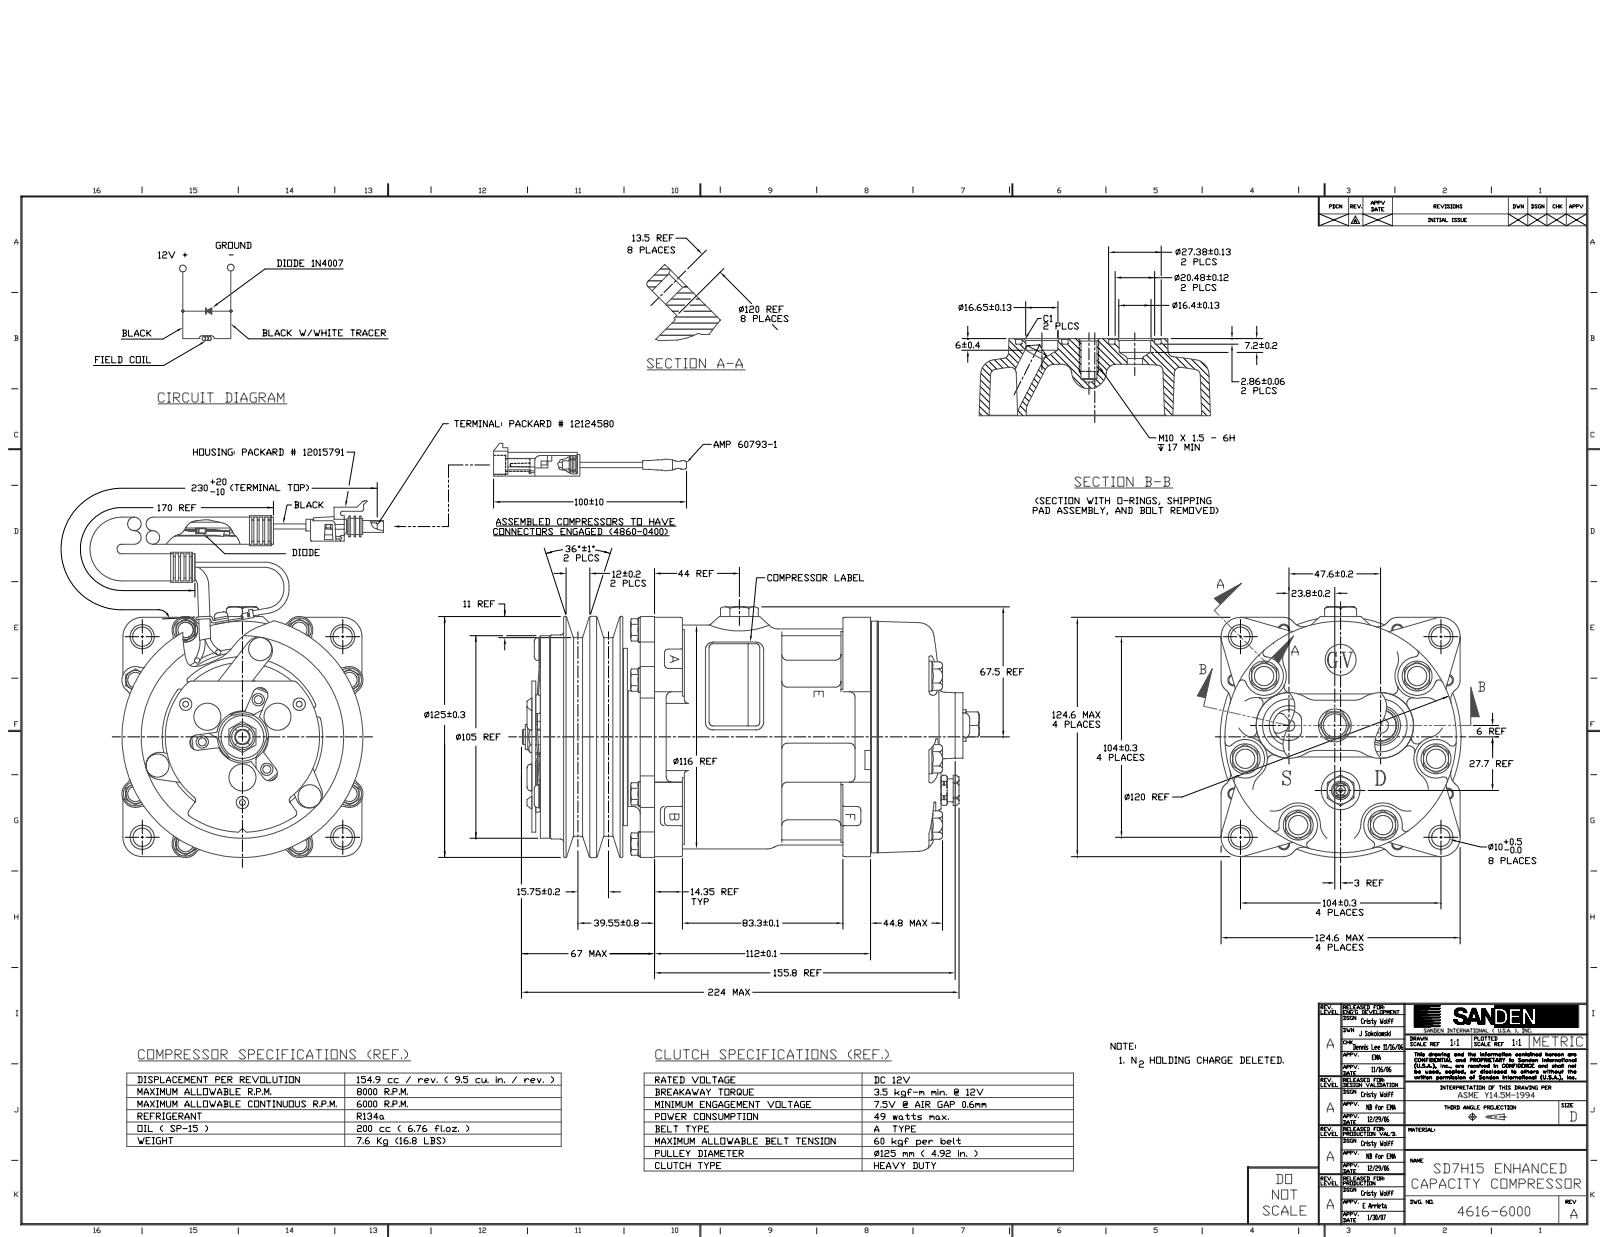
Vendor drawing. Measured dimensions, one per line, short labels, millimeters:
name: SANDEN_4616_REV_A_COMPR_AC
written by: SolidWorks 2007 (CONFIG_CONTROL_DESIGN)
unit: mm
bodies: 1 solid, 2566 faces (743 planar, 707 cylindrical, 1116 other)
size: 438.33 × 226.04 × 125
volume: 2 177 000 mm³; area: 251 890 mm²
holes: 9× ⌀8.5, 8× ⌀5.5, 8× ⌀7, 6× ⌀11.9, 4× ⌀8, 4× ⌀10.25, 3× ⌀2.2, 3× ⌀5.08, 3× ⌀6.6, 2× ⌀27.38, 1× ⌀3.5, 1× ⌀5
bosses: 8× ⌀12.9, 8× ⌀5.69, 6× ⌀15.3, 6× ⌀2.7, 4× ⌀12, 3× ⌀14, 3× ⌀10, 3× ⌀7.9
rounds: 33× R7, 31× R2, 26× R1, 25× R6.5, 24× R3, 19× R5, 13× R4, 12× R1.5
face distances: 2, 5.6, 6.4, 5, 46.54, 39.94, 44.94, 4.4, 33.54, 13
hole spacings: 62.85, 88.89, 36.77, 46.4, 50.77, 59, 111, 120.21
